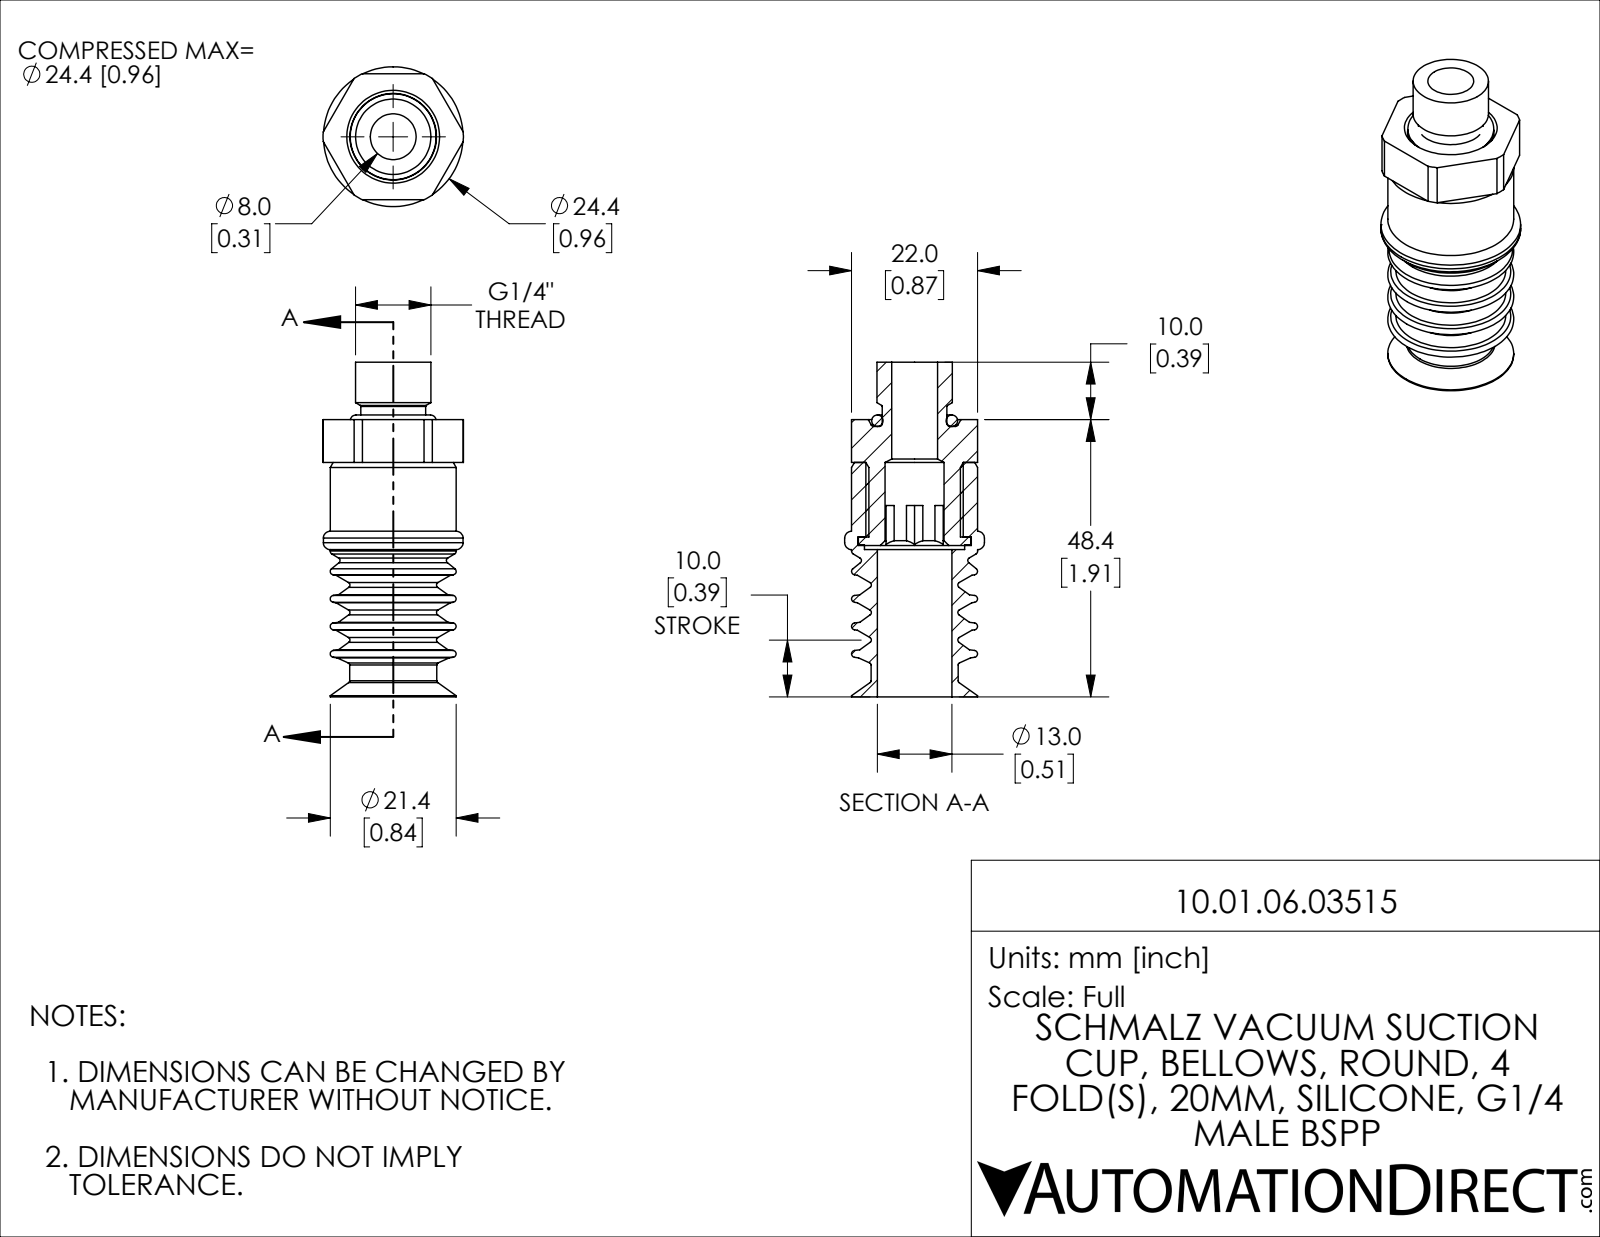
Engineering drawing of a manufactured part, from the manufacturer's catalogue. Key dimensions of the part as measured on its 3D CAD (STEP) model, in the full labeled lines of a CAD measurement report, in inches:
Part name (STEP PRODUCT): 10.01.06.03515
STEP written by: SolidWorks 2021 (CONFIG_CONTROL_DESIGN)
Units: inches
Bodies: 3 solids, 162 faces (35 planar, 37 cylindrical, 90 other)
Overall size (bounding box): 2.299 × 0.965 × 0.961
Volume: 0.729 in³ · Surface area: 15.68 in²
Round holes (diameter × count): ⌀0.315 ×1, ⌀0.406 ×1, ⌀0.512 ×1, ⌀0.63 ×1, ⌀0.689 ×1, ⌀0.772 ×1
Round bosses / shafts (diameter × count): ⌀0.961 ×1, ⌀0.866 ×1, ⌀0.78 ×1, ⌀0.669 ×1, ⌀0.598 ×1, ⌀0.518 ×1, ⌀0.445 ×1
Partial cylindrical surfaces — rounded edges, fillets, slot ends (radius × count): R0.482 ×1
Main face-to-face distances: 0.866, 1.61, 0.295, 1.906, 1.039, 0.571, 1.098, 0.059, 0.512, 0.807
